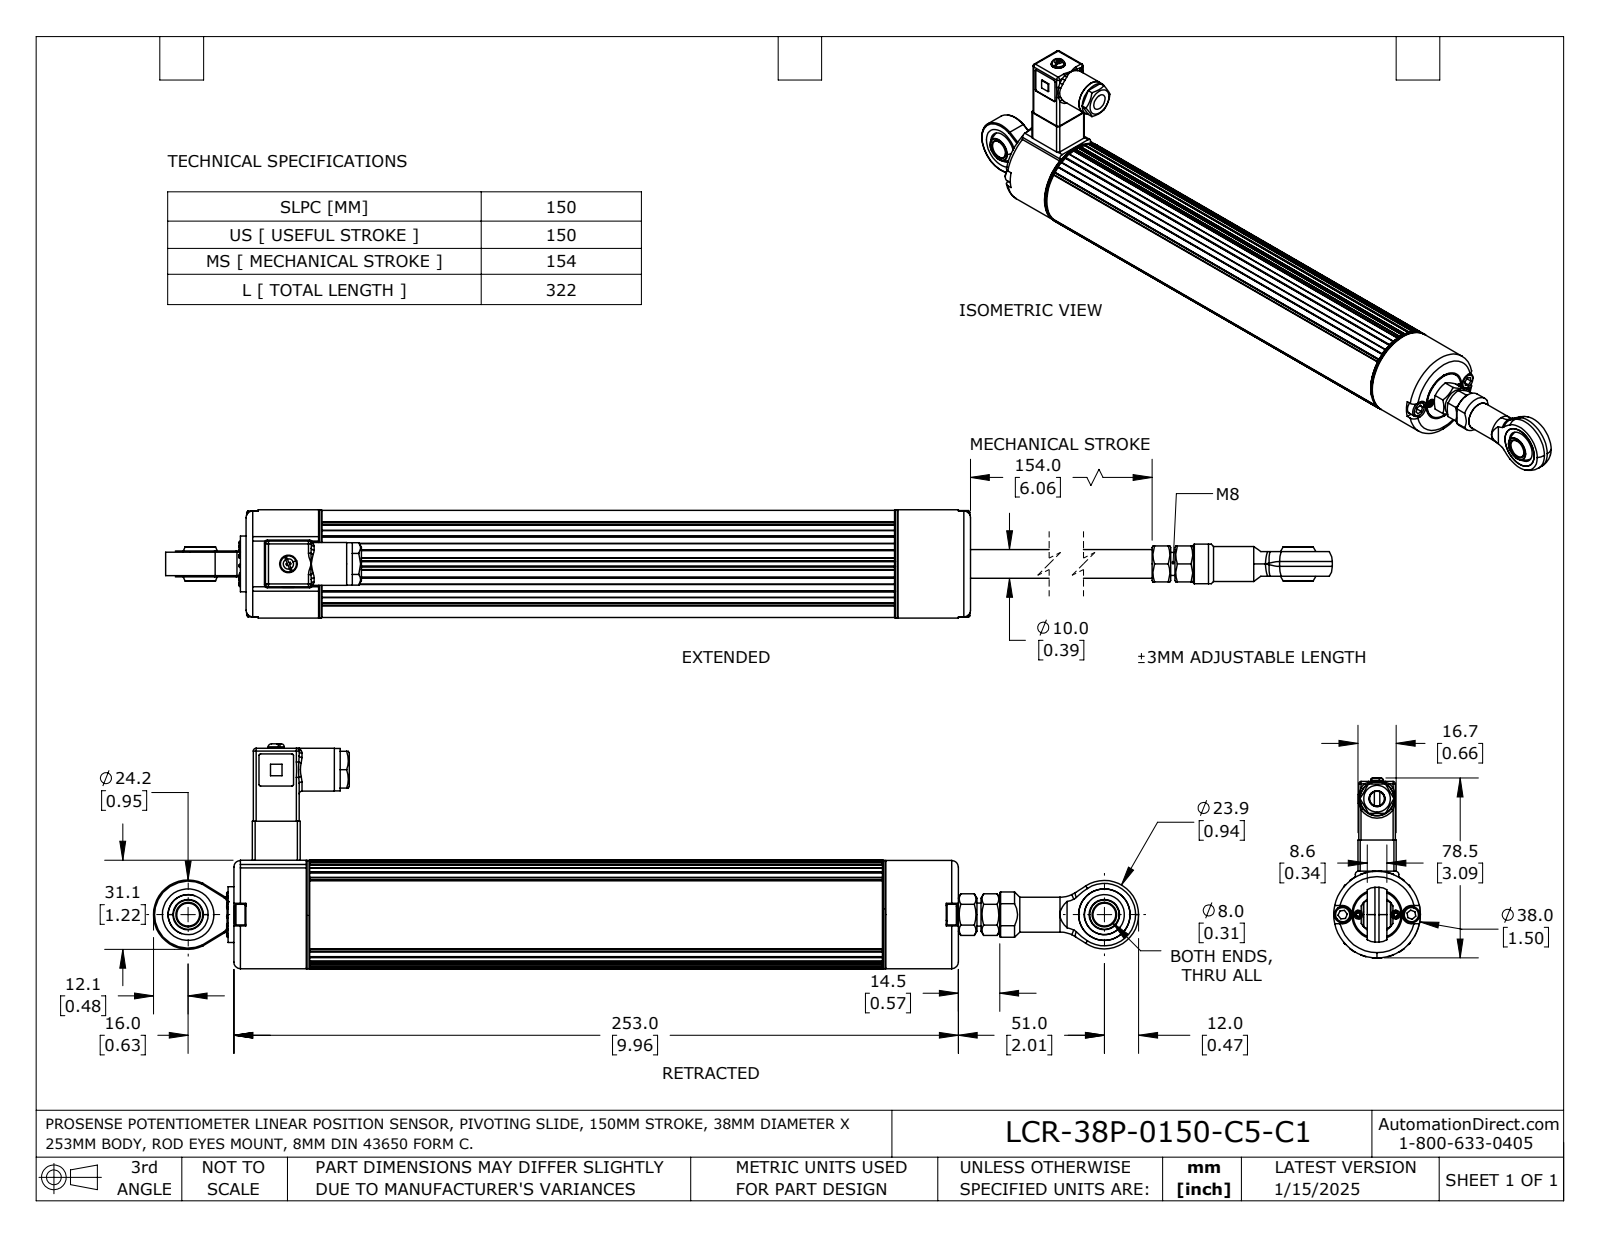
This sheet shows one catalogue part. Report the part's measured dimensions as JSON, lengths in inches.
{"part_name": "LCR-38P-0150-C5-C1", "step_written_by": "SolidWorks 2023 (AUTOMOTIVE_DESIGN)", "units": "inches", "bodies": {"solids": 11, "faces": 657, "planar": 295, "cylindrical": 210, "other": 152}, "overall_size": [13.545, 3.093, 1.488], "volume_in3": 18.32, "surface_area_in2": 97.09, "round_holes": [[0.102, 6], [0.091, 4], [0.315, 3], [0.551, 3], [0.094, 2], [0.1, 2], [0.111, 2], [0.134, 2], [0.152, 2], [0.165, 2], [0.079, 1], [0.118, 1]], "round_bosses_or_shafts": [[0.063, 6], [0.283, 4], [0.15, 4], [0.48, 2], [0.079, 2], [1.488, 1], [0.823, 1], [0.768, 1]], "partial_cylinders_radius": [[0.008, 32], [0.039, 20], [0.02, 12], [0.016, 6], [0.012, 2], [0.059, 2], [0.083, 2], [0.098, 2]], "face_to_face_distances": [7.874, 1.043, 8.917, 0.031, 0.045, 0.612, 0.598, 0.014, 0.644, 0.138], "hole_center_spacings": [0.632, 0.075, 0.634, 0.264, 0.268, 0.285, 0.323, 0.394]}
